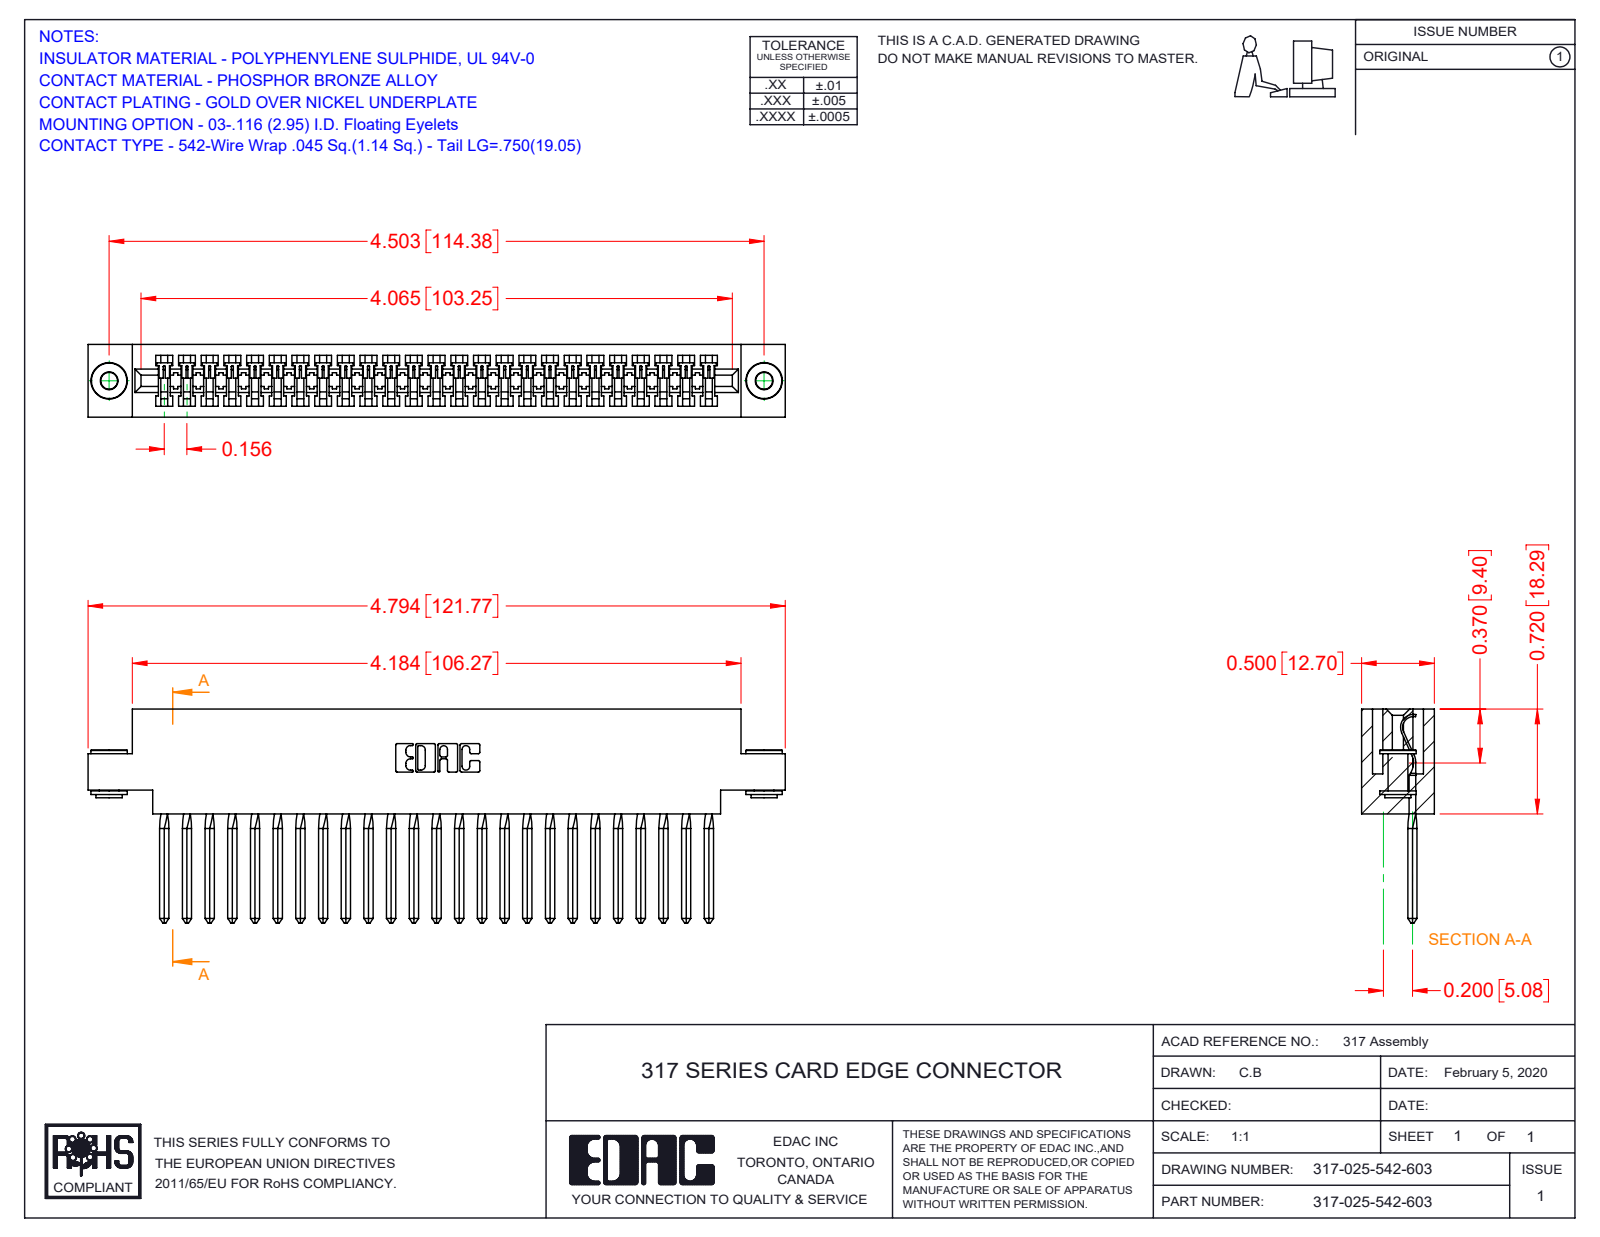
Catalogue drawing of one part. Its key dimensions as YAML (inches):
part_name: "345-250-002_345-250-002-102; 317-025-542-603; 317-290-003_542; 317 Part_.156 Dia - TH"
step_written_by: "SolidWorks 2016 (CONFIG_CONTROL_DESIGN)"
units: inches
bodies: {solids: 28, faces: 2015, planar: 1668, cylindrical: 239, other: 108}
overall_size: [4.794, 1.47, 0.5]
volume: 1.121
surface_area: 34.5
round_holes:
  - {diameter: 0.116, count: 2}
  - {diameter: 0.156, count: 2}
round_bosses_or_shafts:
  - {diameter: 0.25, count: 2}
  - {diameter: 0.18, count: 2}
  - {diameter: 0.136, count: 2}
partial_cylinders:
  - {radius: 0.006, count: 50}
  - {radius: 0.01, count: 22}
  - {radius: 0.007, count: 6}
  - {radius: 0.031, count: 6}
  - {radius: 0.026, count: 3}
  - {radius: 0.074, count: 1}
  - {radius: 0.089, count: 1}
  - {radius: 0.1, count: 1}
face_to_face_distances: [0.5, 0.075, 0.425, 0.35, 0.11, 0.136, 0.72, 0.211, 0.289, 0.213]
hole_center_spacings: [4.503]
